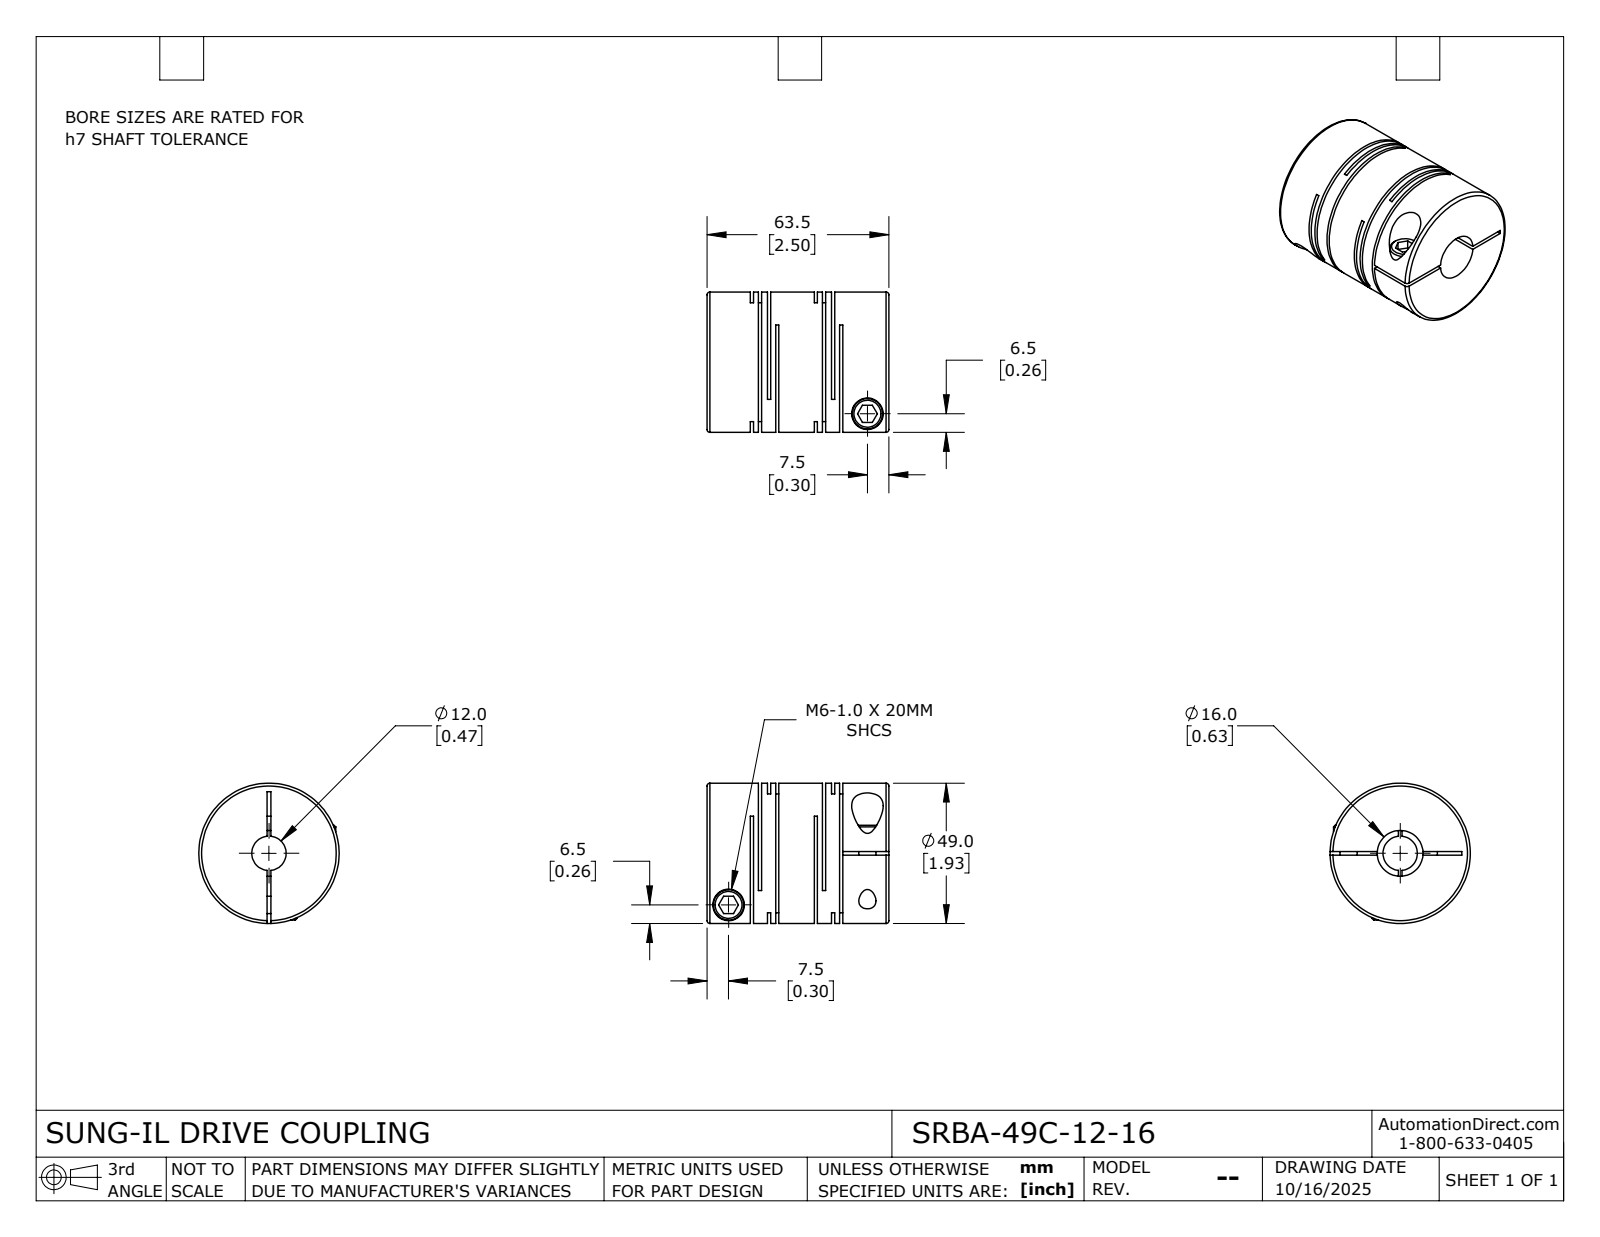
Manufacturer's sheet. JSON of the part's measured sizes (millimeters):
{"part_name": "SRBA-49C-12-16", "step_written_by": "SolidWorks 2024 (CONFIG_CONTROL_DESIGN)", "units": "millimeters", "bodies": {"solids": 1, "faces": 115, "planar": 60, "cylindrical": 42, "other": 13}, "overall_size": [63.5, 49, 49], "volume_mm3": 93483, "surface_area_mm2": 39650, "round_holes": [[6, 2], [11, 2], [12, 1], [16, 1]], "round_bosses_or_shafts": [[10.6, 2], [49, 1]], "face_to_face_distances": [6, 1.1, 22.35, 2.85, 21.25, 3.15, 1.75, 4.9, 19.5, 16.35]}
